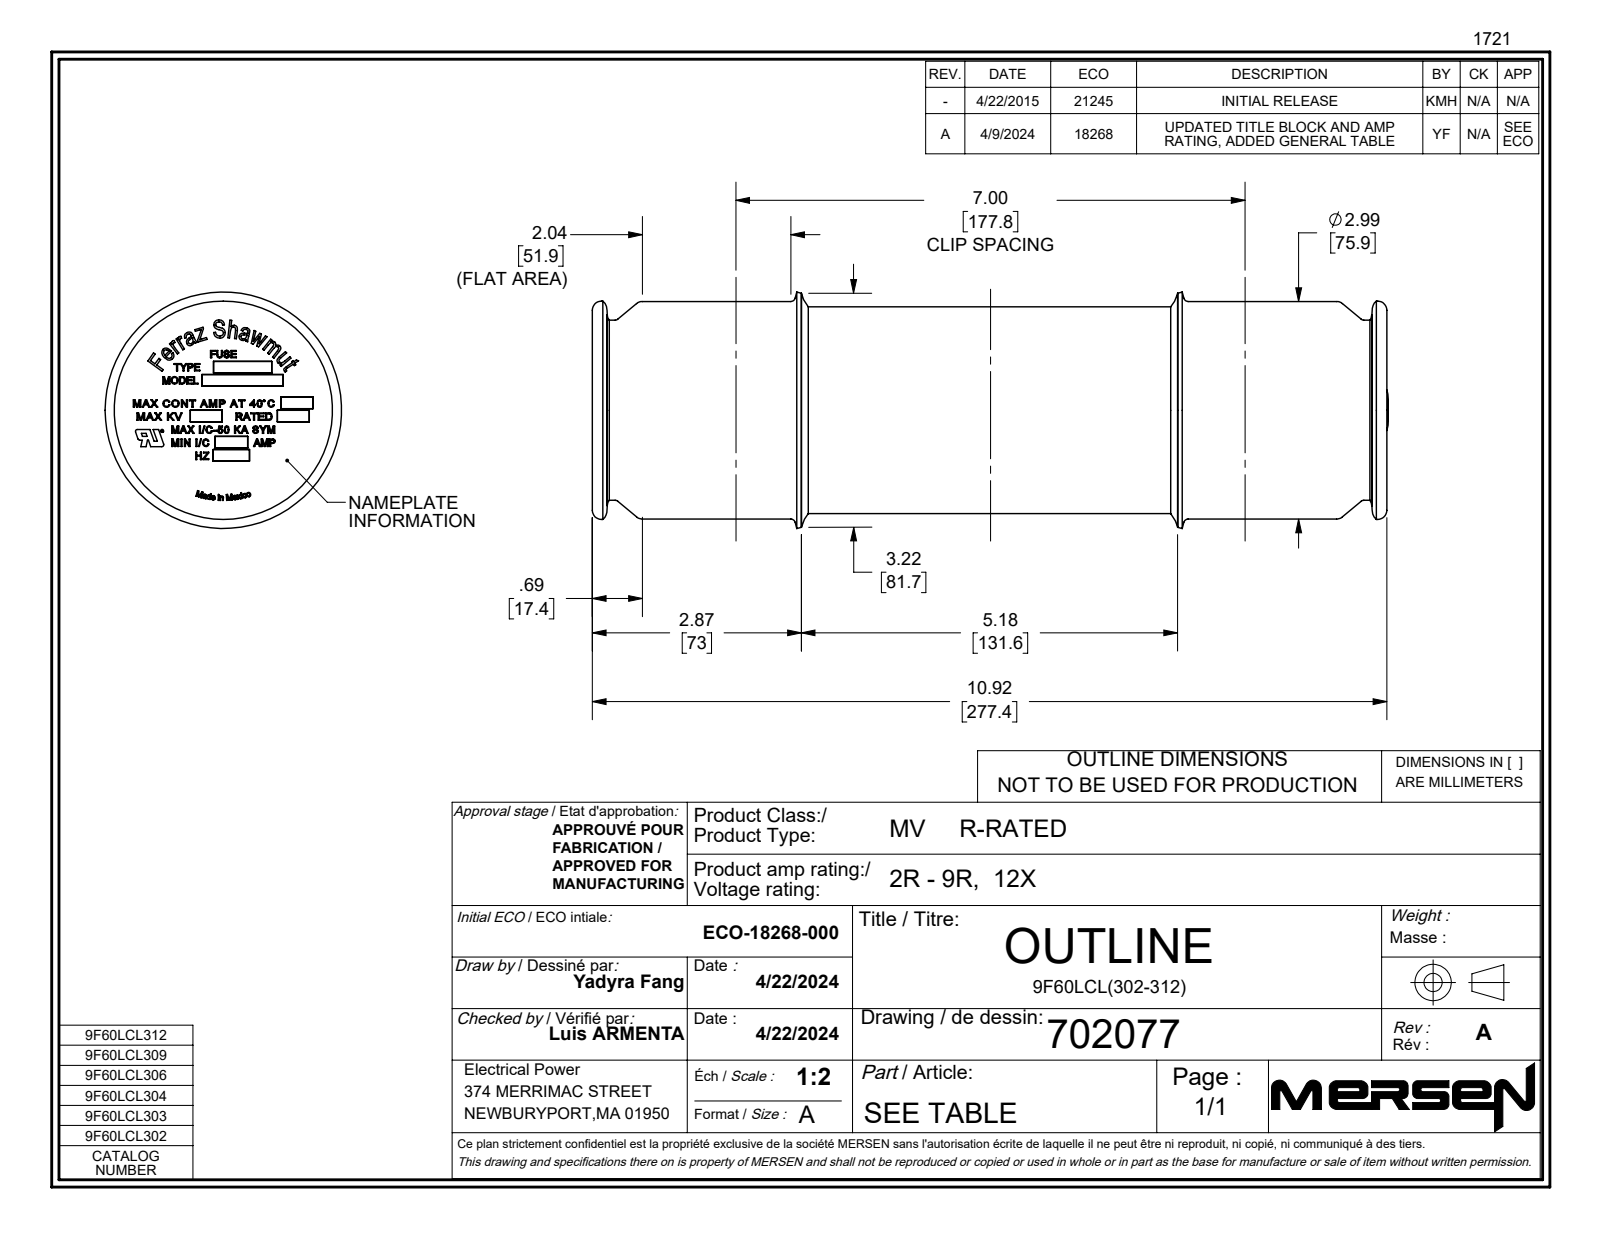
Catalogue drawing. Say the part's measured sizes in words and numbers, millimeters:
The part is named "702077; 2A603022_P01 CRIMPED; 2A600022_CRIMPED; Part1^2B601037FG01 (+6 more)". Its 3-D file was written by "SolidWorks 2021 (AUTOMOTIVE_DESIGN)". It is 10 solids with 1503 faces: 949 planar, 55 cylindrical and 499 other. Overall it measures 278 by 82.6 by 82.6 millimeters. Its volume is 194 000 cubic millimeters and its surface area 268 000 square millimeters. Round holes: 1 of diameter 1, 1 of diameter 9.5, 1 of diameter 59.6, 1 of diameter 62.9, 1 of diameter 68.3, 1 of diameter 72, 1 of diameter 72.2, 1 of diameter 72.6. Round bosses or shafts: 1 of diameter 76.2, 1 of diameter 75.9, 1 of diameter 72, 1 of diameter 11, 1 of diameter 9.5. Partial cylindrical surfaces (rounded edges, fillets, slot ends): 3 of radius 0.7. The main face-to-face distances are 1.6, 275.8, 277.4, 274.3, 275.9, 1.6, 1.7, 272.6, 1.7, 3.3. The hole center spacings are 22.6.
